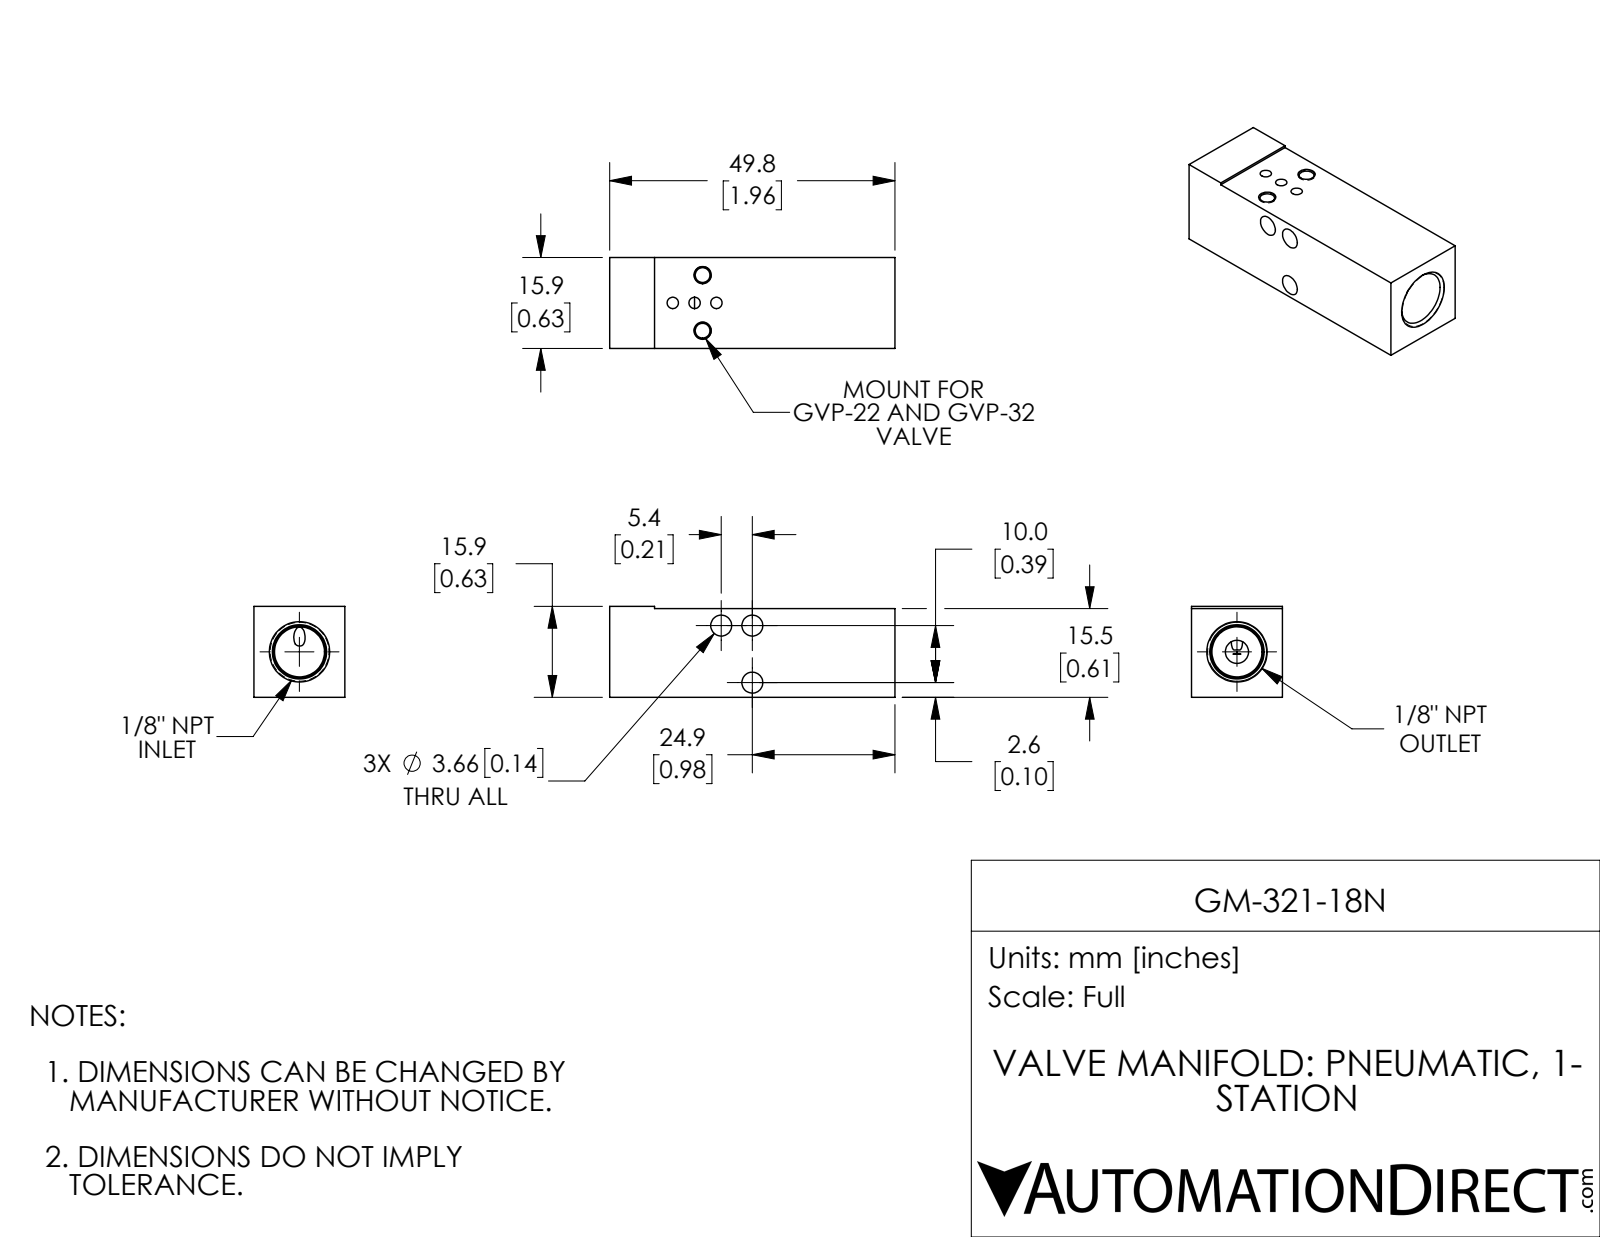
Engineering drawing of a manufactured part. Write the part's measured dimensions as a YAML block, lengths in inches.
part_name: "GM-321-18N"
step_written_by: "SolidWorks 2018 (AUTOMOTIVE_DESIGN)"
units: inches
bodies: {solids: 1, faces: 56, planar: 10, cylindrical: 23, other: 23}
overall_size: [1.962, 0.625, 0.625]
volume: 0.576
surface_area: 8.247
round_holes:
  - {diameter: 0.078, count: 3}
  - {diameter: 0.144, count: 3}
  - {diameter: 0.101, count: 2}
  - {diameter: 0.159, count: 1}
  - {diameter: 0.344, count: 1}
face_to_face_distances: [0.625, 0.61, 1.962, 0.015, 0.273, 1.689, 0.308, 1.654, 1.381, 0.035]
hole_center_spacings: [0.15, 0.199, 0.213, 0.28, 0.214, 0.3, 0.382, 0.392]
